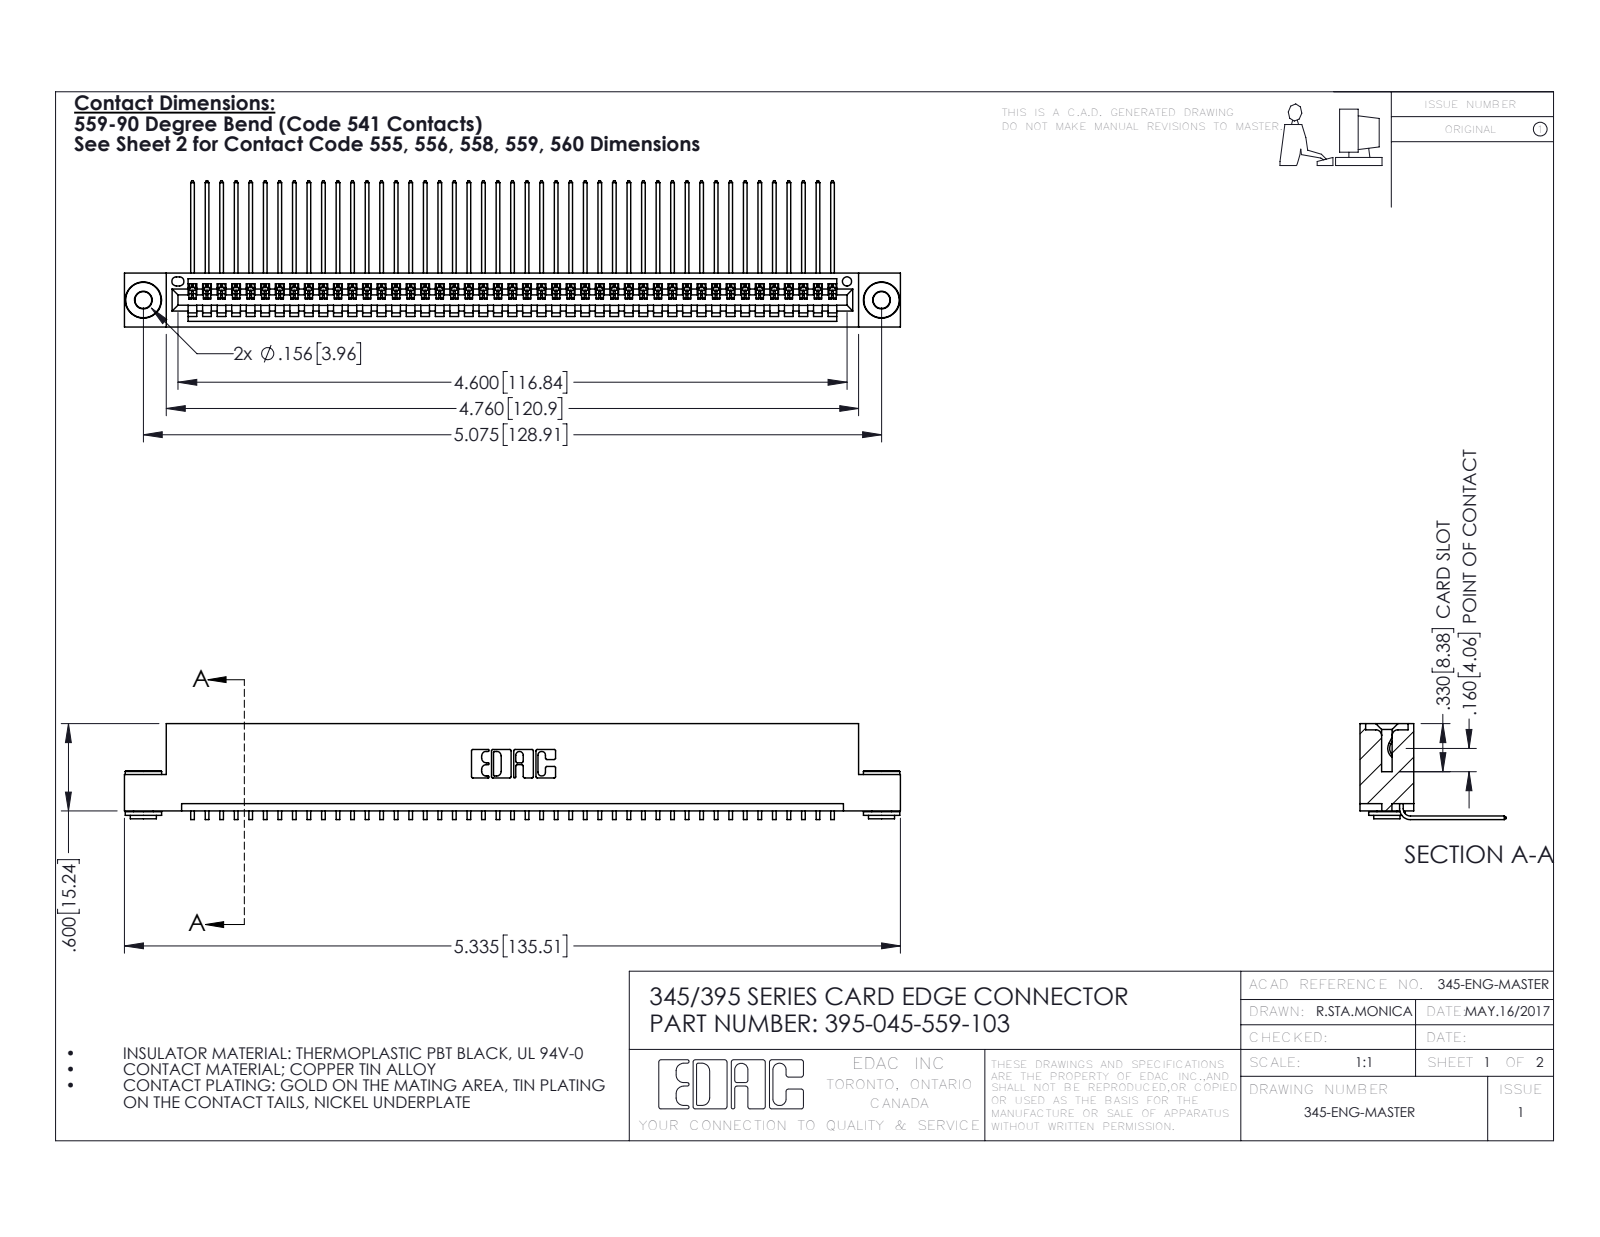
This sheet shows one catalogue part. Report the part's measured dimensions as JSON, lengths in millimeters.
{"part_name": "395-045-559-103; 345-250-002_345-250-002-102; 345-292-001_558 559 Tail - 1; 345 Part_Flush Mounting Lugs - 0.156 Dia-TH", "step_written_by": "SolidWorks 2016 (CONFIG_CONTROL_DESIGN)", "units": "millimeters", "bodies": {"solids": 48, "faces": 2864, "planar": 1980, "cylindrical": 876, "other": 8}, "overall_size": [135.5, 25.5, 16.7], "volume_mm3": 13100, "surface_area_mm2": 18500, "round_holes": [[2.9, 2], [4, 2], [1.6, 1]], "round_bosses_or_shafts": [[6.4, 2], [4.6, 2], [3.5, 2]], "partial_cylinders_radius": [[0.2, 90], [0.3, 22], [0.2, 6], [0.8, 6], [0.7, 3], [0.8, 2], [1, 2], [0.4, 1]], "face_to_face_distances": [1.8, 7.6, 9.4, 5.1, 0.6, 2.5, 6.9, 5.7, 3.8, 1.8], "hole_center_spacings": [6.9, 122.9, 128.9]}
